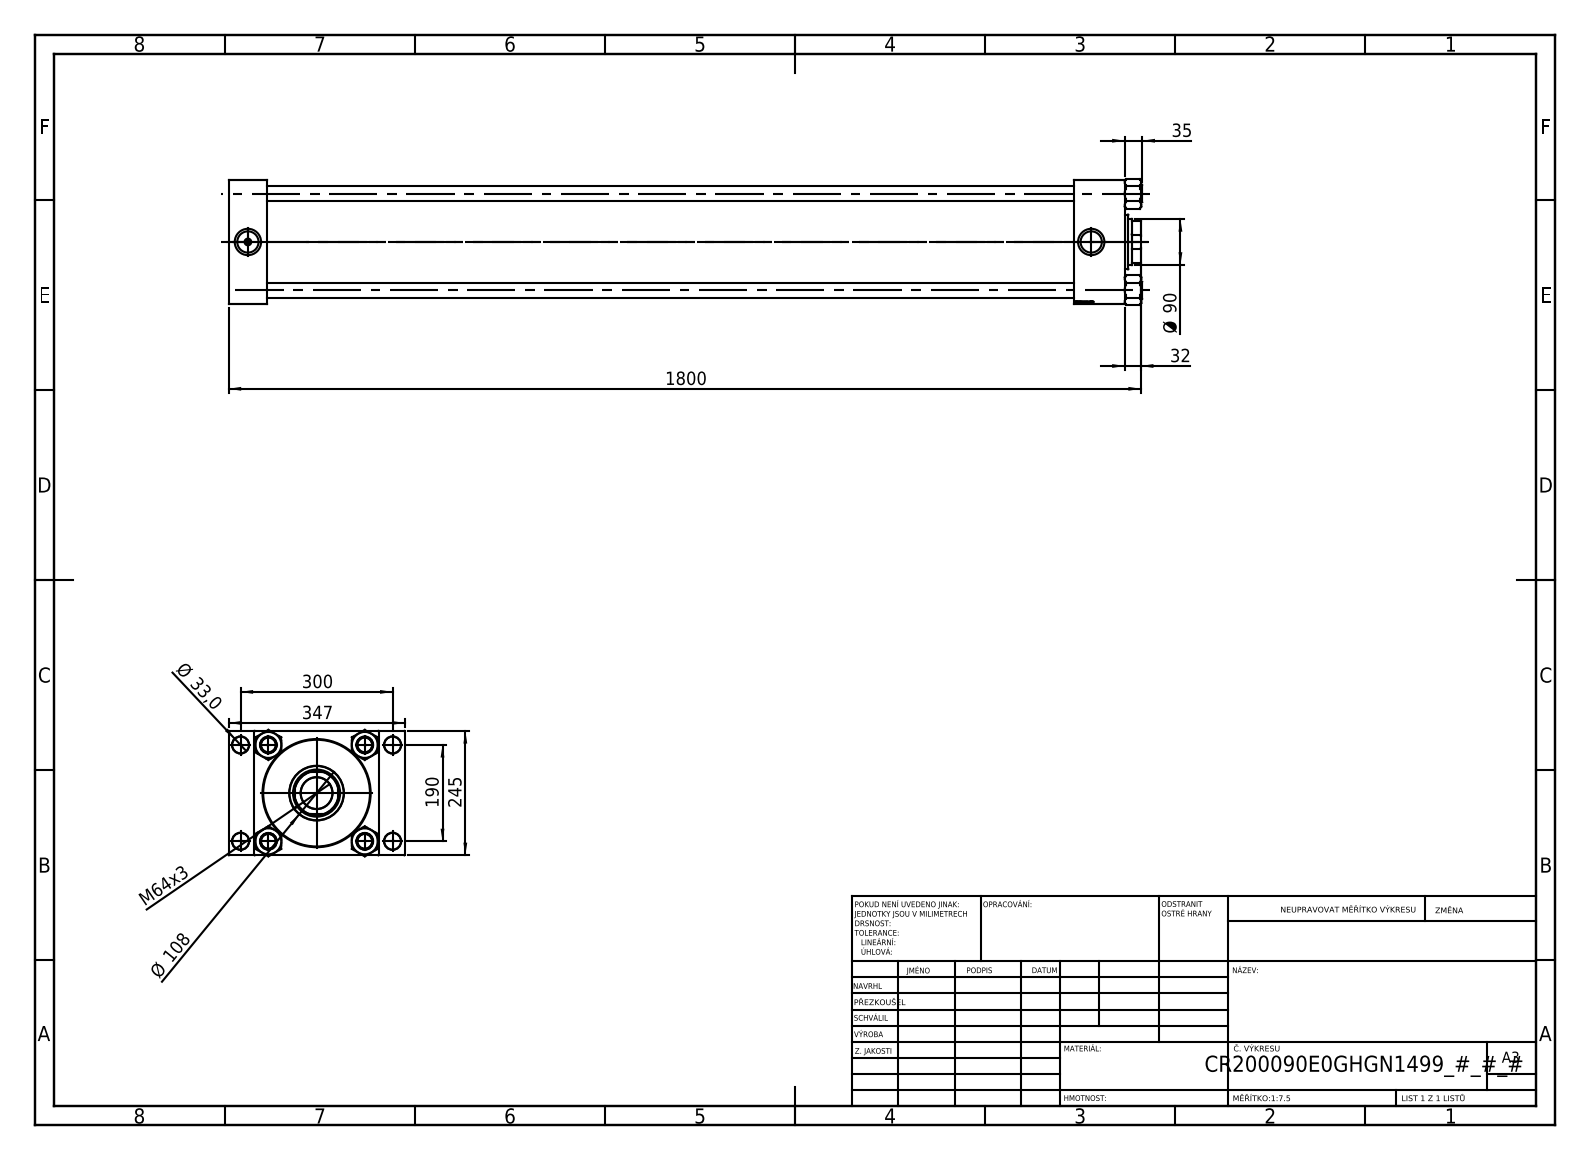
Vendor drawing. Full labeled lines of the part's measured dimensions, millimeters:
Part name (STEP PRODUCT): V215CR_VCP_E; NUT_M5_E; V215_VC_A; V215CR_TYCINKA_E (+1 more)
STEP written by: SolidWorks 2019 (CONFIG_CONTROL_DESIGN)
Units: millimetres
Bodies: 11 solids, 1184 faces (546 planar, 86 cylindrical, 552 other)
Overall size (bounding box): 1803 × 347 × 249.44
Volume: 31 530 000 mm³ · Surface area: 4 025 000 mm²
Round holes (diameter × count): ⌀30 ×4, ⌀33 ×4, ⌀7 ×2, ⌀41.92 ×2, ⌀52 ×2, ⌀62.5 ×1, ⌀90 ×1, ⌀93 ×1, ⌀146 ×1, ⌀200 ×1, ⌀210.5 ×1
Round bosses / shafts (diameter × count): ⌀33 ×4, ⌀206 ×1, ⌀108 ×1
Partial cylindrical surfaces — rounded edges, fillets, slot ends (radius × count): R44 ×1
Main face-to-face distances: 76, 245, 1768, 1692, 1739.3, 1663.3, 28.7, 1667, 1591, 72.3
Hole centre spacings: 54.9, 134.49, 177.55, 190.2, 197.87, 245.1, 310.18, 190
